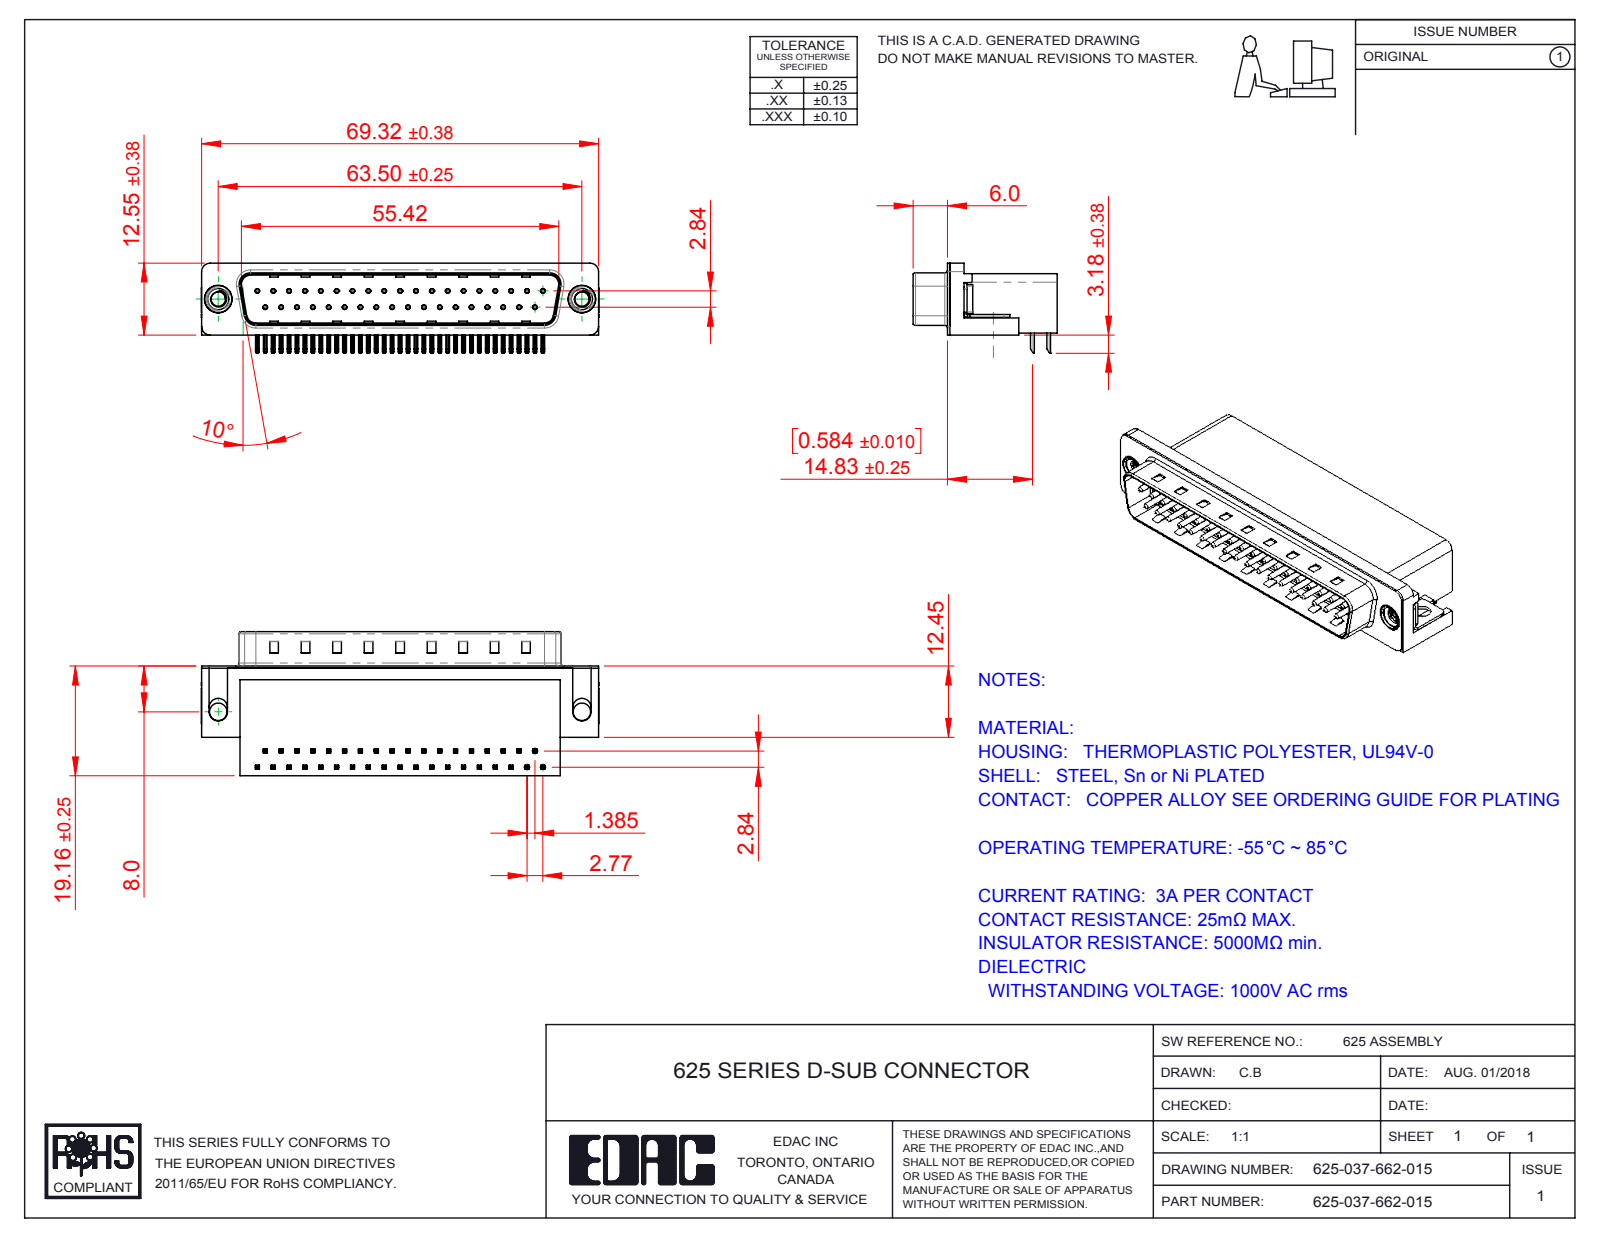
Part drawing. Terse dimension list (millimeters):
name: 625-037-662-015; 625 Contact Bottom; 625 Shell_37 Socket; 625 M3 Threaded Rivet (+3 more)
written by: SolidWorks 2016 (CONFIG_CONTROL_DESIGN)
unit: mm
bodies: 43 solids, 3201 faces (2013 planar, 921 cylindrical, 267 other)
size: 69.4 × 25.16 × 15.73
volume: 12 593 mm³; area: 11 745 mm²
holes: 37× ⌀0.35, 37× ⌀0.8, 2× ⌀2.5, 2× ⌀3.05, 2× ⌀4, 2× ⌀4.8, 2× ⌀5
bosses: 37× ⌀0.75, 2× ⌀4.9, 2× ⌀4.75, 2× ⌀3.9
rounds: 156× R0.25, 74× R0.12, 16× R1, 9× R0.5, 8× R1.6, 7× R1.5, 4× R0.9, 4× R2
face distances: 10.34, 0.4, 18.76, 8.76, 19.16, 2.84, 2.09, 10.1, 1.74, 8.36
hole spacings: 3.16, 2.77, 5.54, 8.31, 11.08, 13.85, 19.39, 22.16
